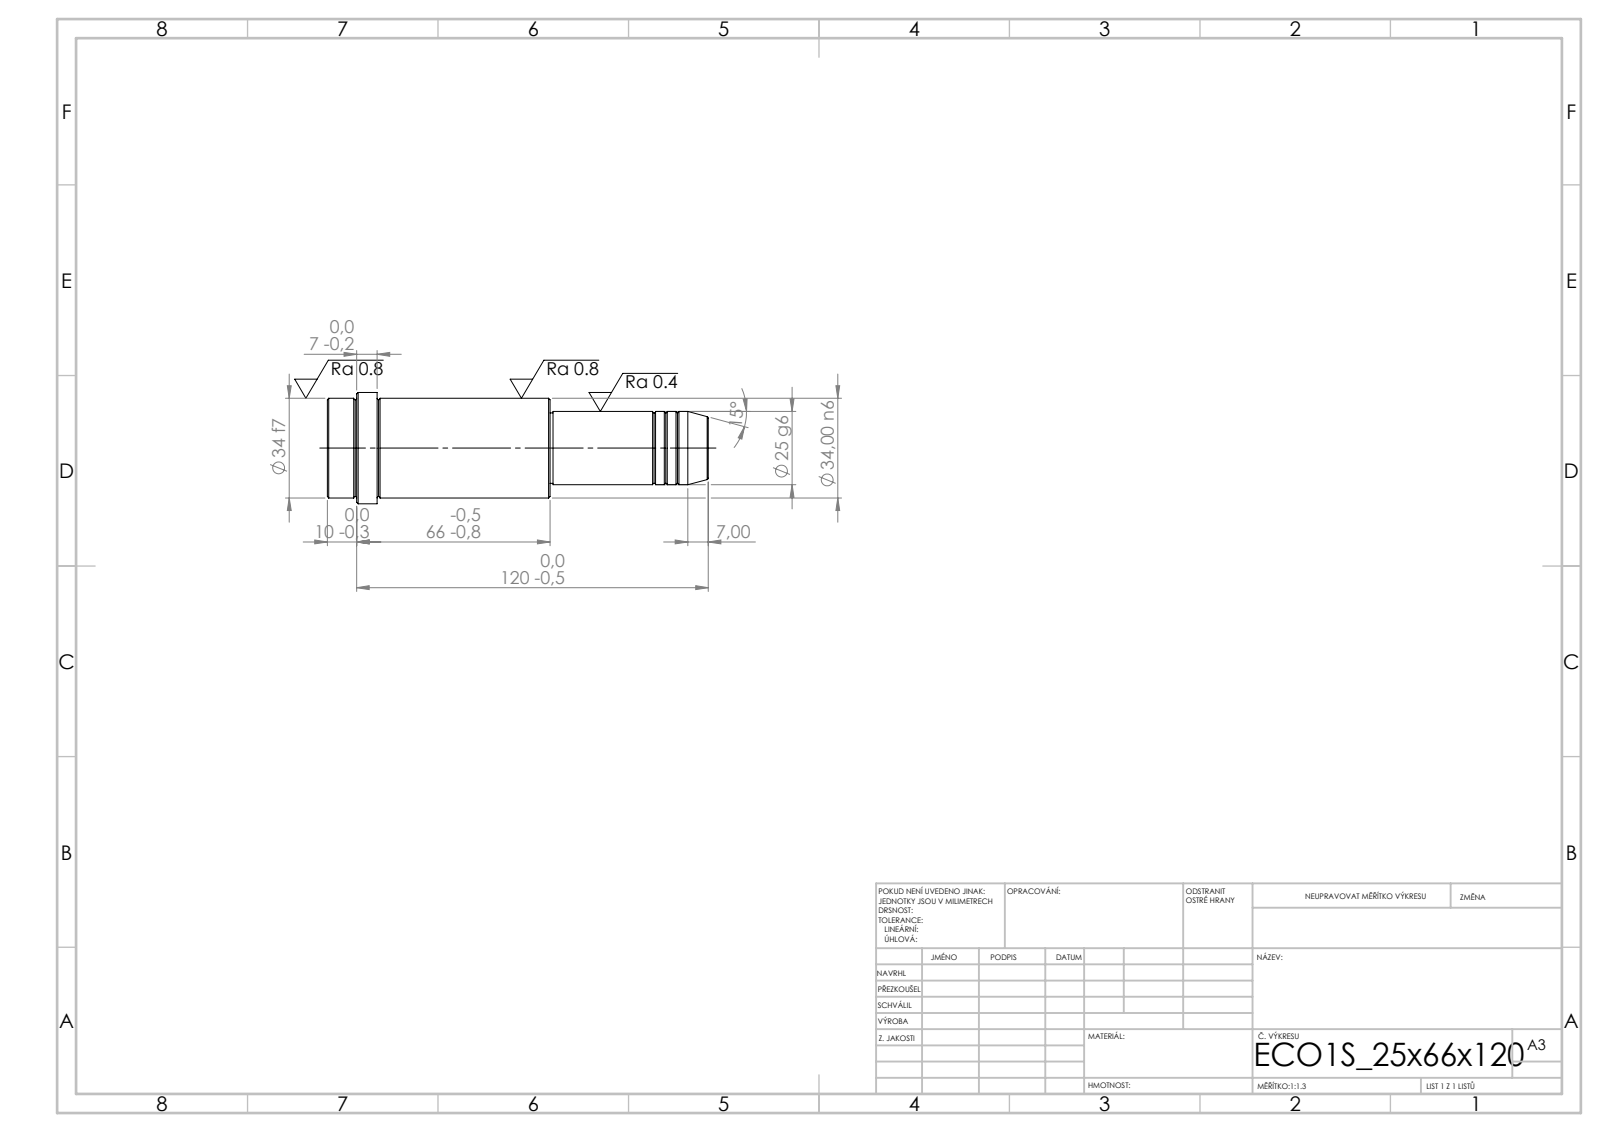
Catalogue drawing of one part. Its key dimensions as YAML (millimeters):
step_written_by: "SolidWorks 2019 (CONFIG_CONTROL_DESIGN)"
units: millimeters
bodies: {solids: 1, faces: 52, planar: 6, cylindrical: 16, other: 30}
overall_size: [130, 38, 38]
volume: 96347
surface_area: 14764
round_bosses_or_shafts:
  - {diameter: 38, count: 1}
  - {diameter: 34, count: 1}
  - {diameter: 25, count: 1}
  - {diameter: 24, count: 1}
face_to_face_distances: [76, 54, 130, 113, 59, 17, 120, 66, 7, 10]
